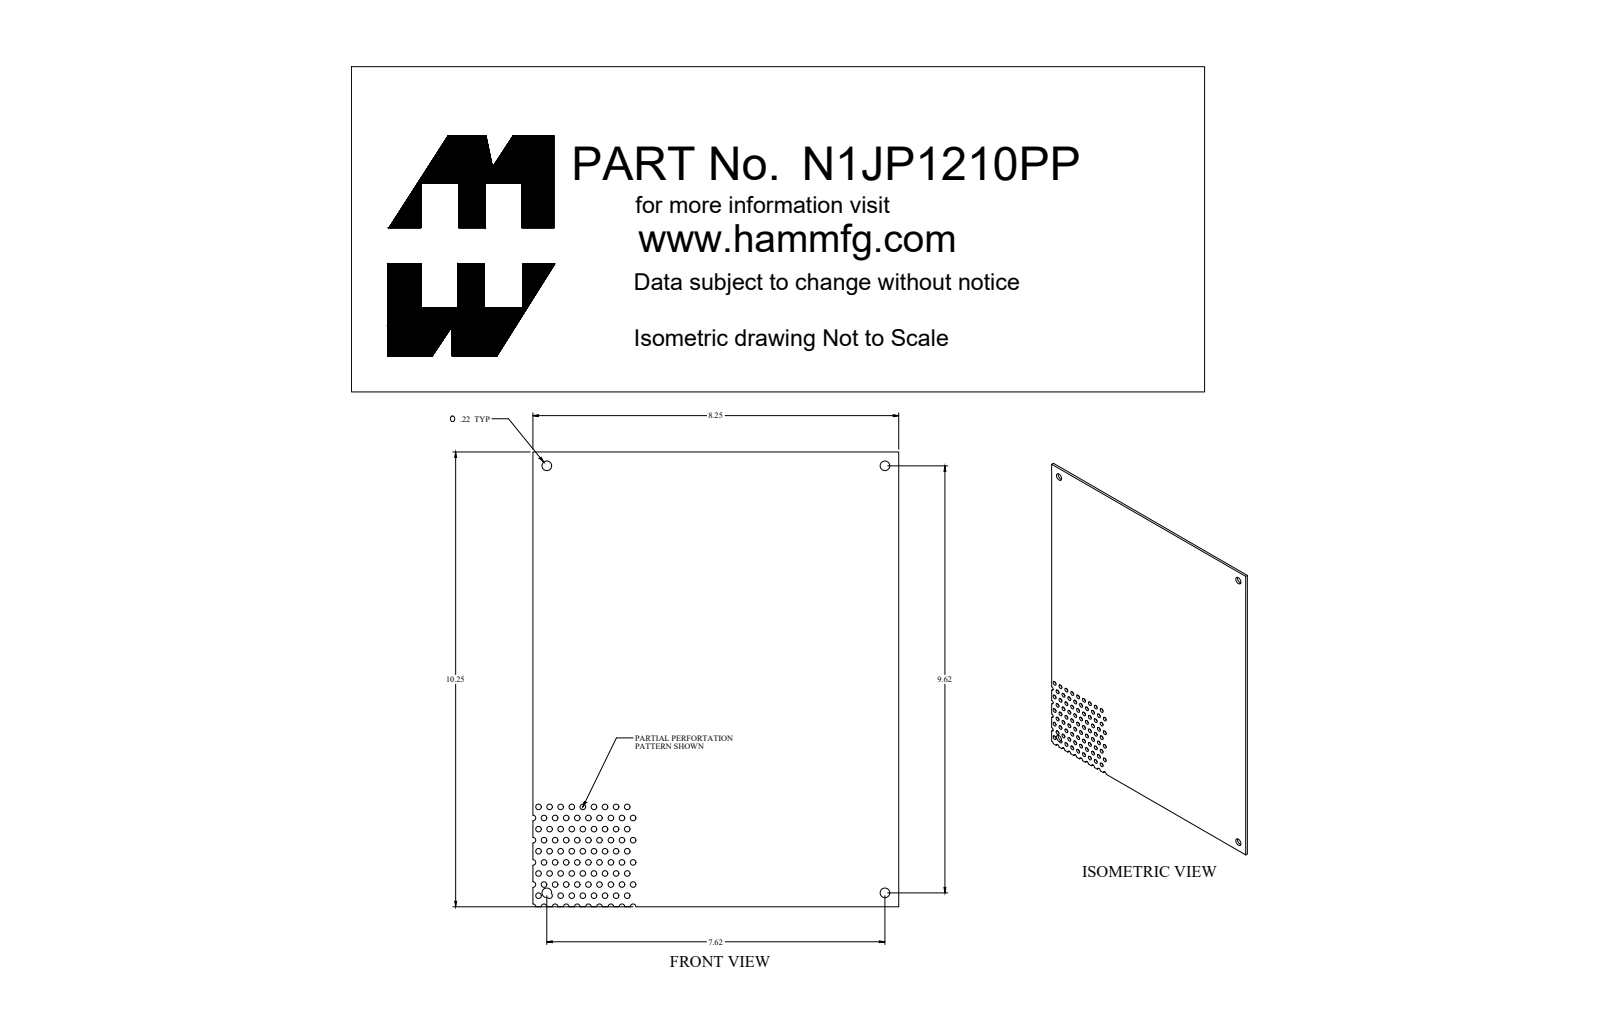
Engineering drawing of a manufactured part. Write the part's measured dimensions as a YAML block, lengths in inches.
part_name: "N1JP1210PP"
step_written_by: "SolidWorks 2018 (AUTOMOTIVE_DESIGN)"
units: inches
bodies: {solids: 1, faces: 203, planar: 19, cylindrical: 184, other: 0}
overall_size: [10.25, 8.25, 0.072]
volume: 6.001
surface_area: 171.9
round_holes:
  - {diameter: 0.125, count: 58}
  - {diameter: 0.125, count: 22}
  - {diameter: 0.218, count: 4}
partial_cylinders:
  - {radius: 0.063, count: 12}
  - {radius: 0.062, count: 3}
face_to_face_distances: [0.072, 8.25, 10.25]
hole_center_spacings: [0.5, 0.28, 0.25, 0.559, 0.707, 0.75, 0.45, 0.902]
